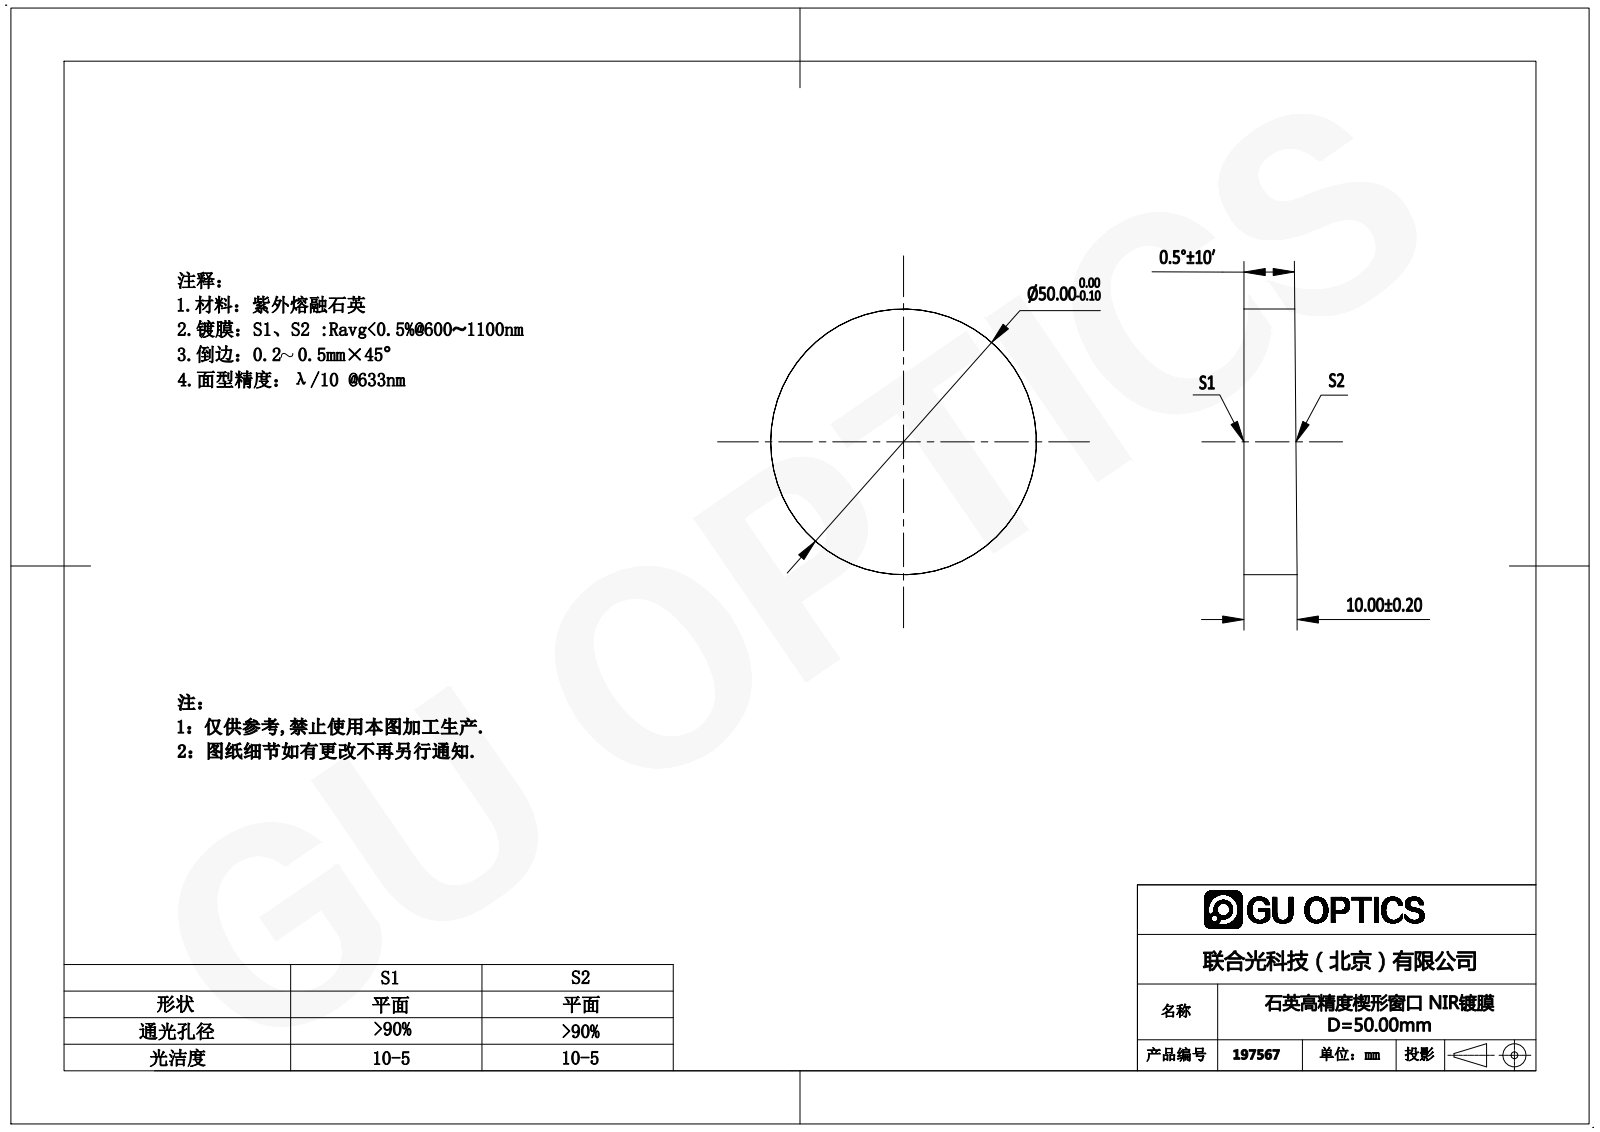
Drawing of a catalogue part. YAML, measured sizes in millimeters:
part_name: "197505"
step_written_by: "SolidWorks 2016 (AUTOMOTIVE_DESIGN)"
units: millimeters
bodies: {solids: 1, faces: 4, planar: 2, cylindrical: 2, other: 0}
overall_size: [50, 50, 10]
volume: 19207
surface_area: 5464
round_bosses_or_shafts:
  - {diameter: 50, count: 1}
